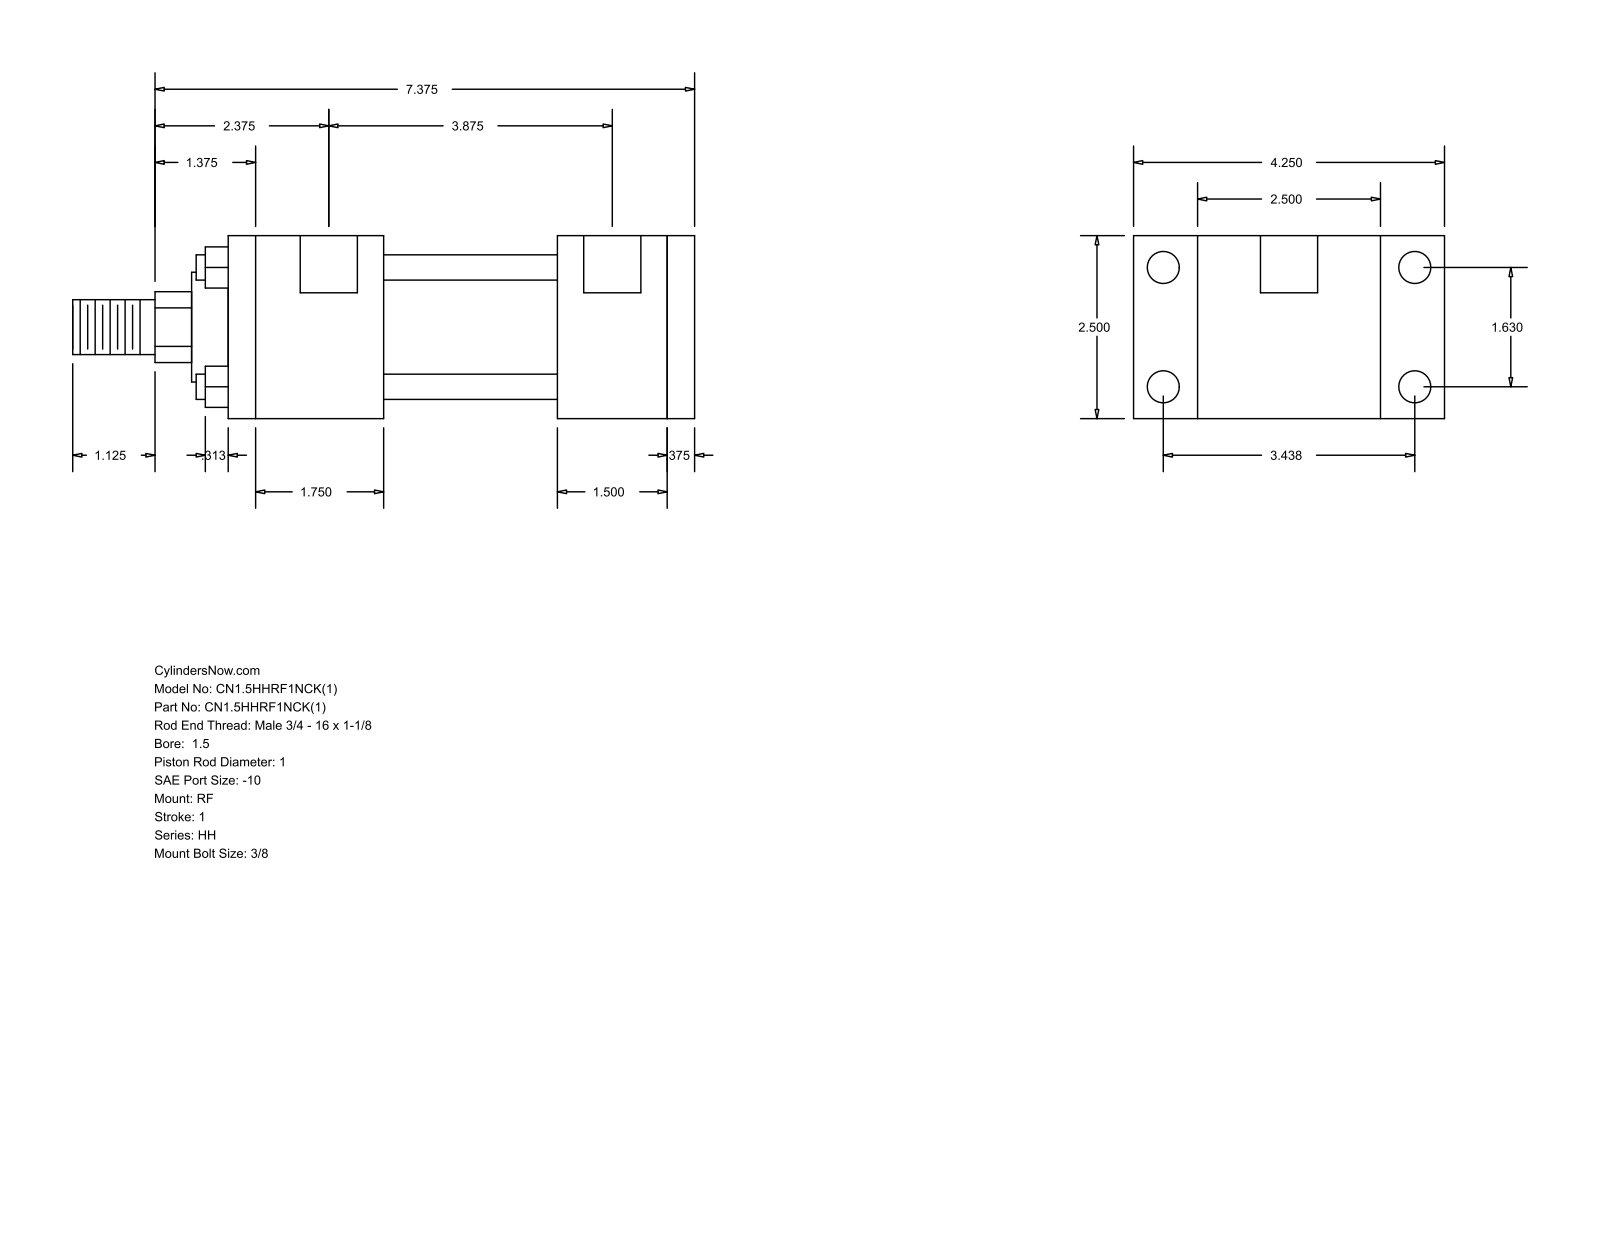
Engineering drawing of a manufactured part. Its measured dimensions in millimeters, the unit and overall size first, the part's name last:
Units: millimetres
Overall size (bounding box): 215.9 × 107.95 × 63.5
Round holes (diameter × count): ⌀5.56 ×4, ⌀11.13 ×4, ⌀19.84 ×2
Round bosses / shafts (diameter × count): ⌀8.76 ×4, ⌀44.45 ×1, ⌀38.1 ×1, ⌀25.4 ×1, ⌀19.05 ×1
Partial cylindrical surfaces — rounded edges, fillets, slot ends (radius × count): R12.29 ×1
Main face-to-face distances: 63.5, 9.52, 38.1, 60.32, 98.42, 107.94, 47.62, 53.98, 114.3, 152.4
Hole centre spacings: 1.59, 41.4, 87.32, 96.64, 100.01, 101.6, 98.42
Bodies: 0 solids, 92 faces (64 planar, 28 cylindrical, 0 other)
Part name (STEP PRODUCT): HH_RF__0150_1
STEP written by: GSSL Pune (CONFIG_CONTROL_DESIGN)
